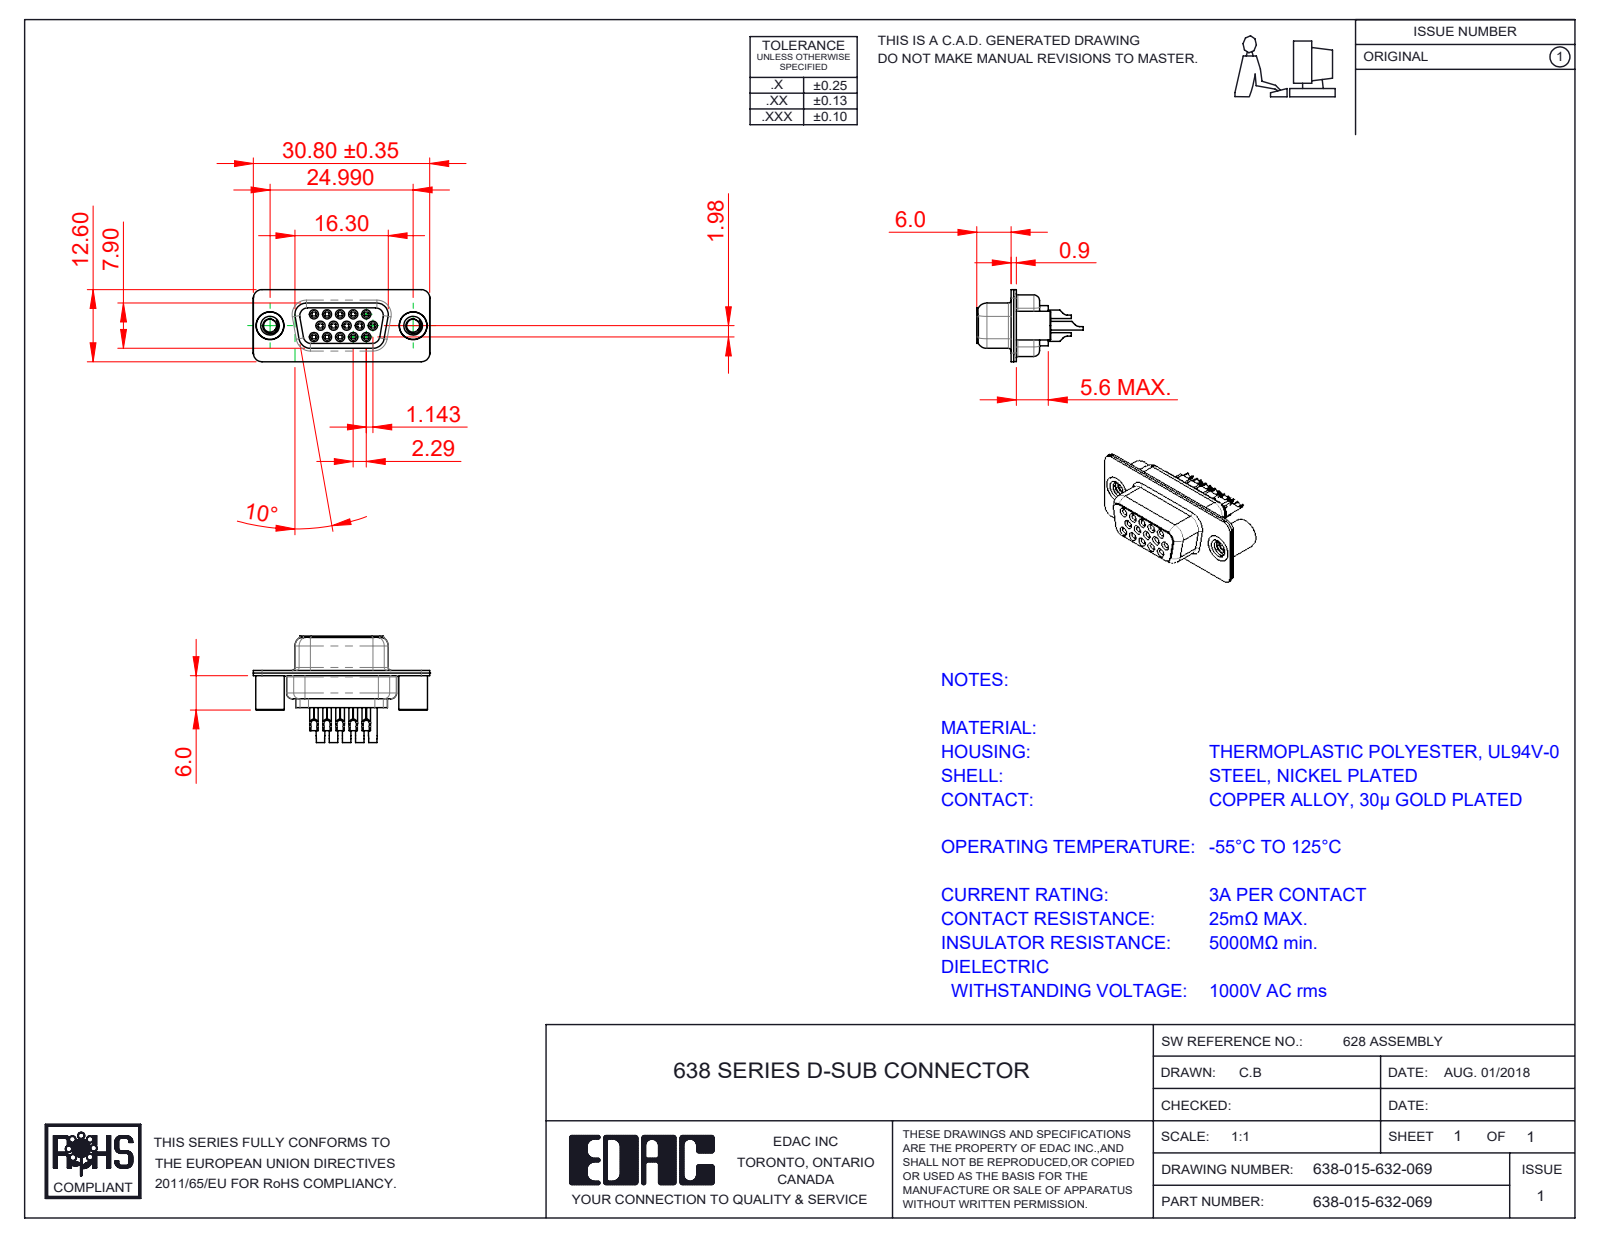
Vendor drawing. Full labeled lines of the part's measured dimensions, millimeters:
Part name (STEP PRODUCT): 638-015-632-069; 638 Contact Row 1_32; 638 Housing_15 Contacts; 638 Contact Row 3_32 (+4 more)
STEP written by: SolidWorks 2020 (CONFIG_CONTROL_DESIGN)
Units: millimetres
Bodies: 20 solids, 1636 faces (382 planar, 532 cylindrical, 722 other)
Overall size (bounding box): 30.81 × 18.6 × 12.6
Volume: 1 699 mm³ · Surface area: 6 050 mm²
Round holes (diameter × count): ⌀0.8 ×15, ⌀1 ×15, ⌀1.1 ×15, ⌀1.6 ×15, ⌀1.7 ×15, ⌀1.8 ×15, ⌀2 ×2, ⌀2.26 ×2, ⌀4 ×2, ⌀4.05 ×2, ⌀4.85 ×2
Round bosses / shafts (diameter × count): ⌀2 ×15, ⌀1.5 ×15, ⌀1.2 ×15, ⌀5 ×2, ⌀4.95 ×2, ⌀4.8 ×2
Partial cylindrical surfaces — rounded edges, fillets, slot ends (radius × count): R1.5 ×20, R2 ×12, R0.28 ×10, R1.55 ×8, R1 ×7, R1.35 ×5, R0.25 ×4, R0.5 ×4
Main face-to-face distances: 0.45, 0.9, 0.4, 1.43, 8.88, 6.6, 1.4, 2.28, 0.85, 6.5
Hole centre spacings: 3.96, 2.28, 4.57, 2.29, 6.05, 6.04, 6.86, 7.92
